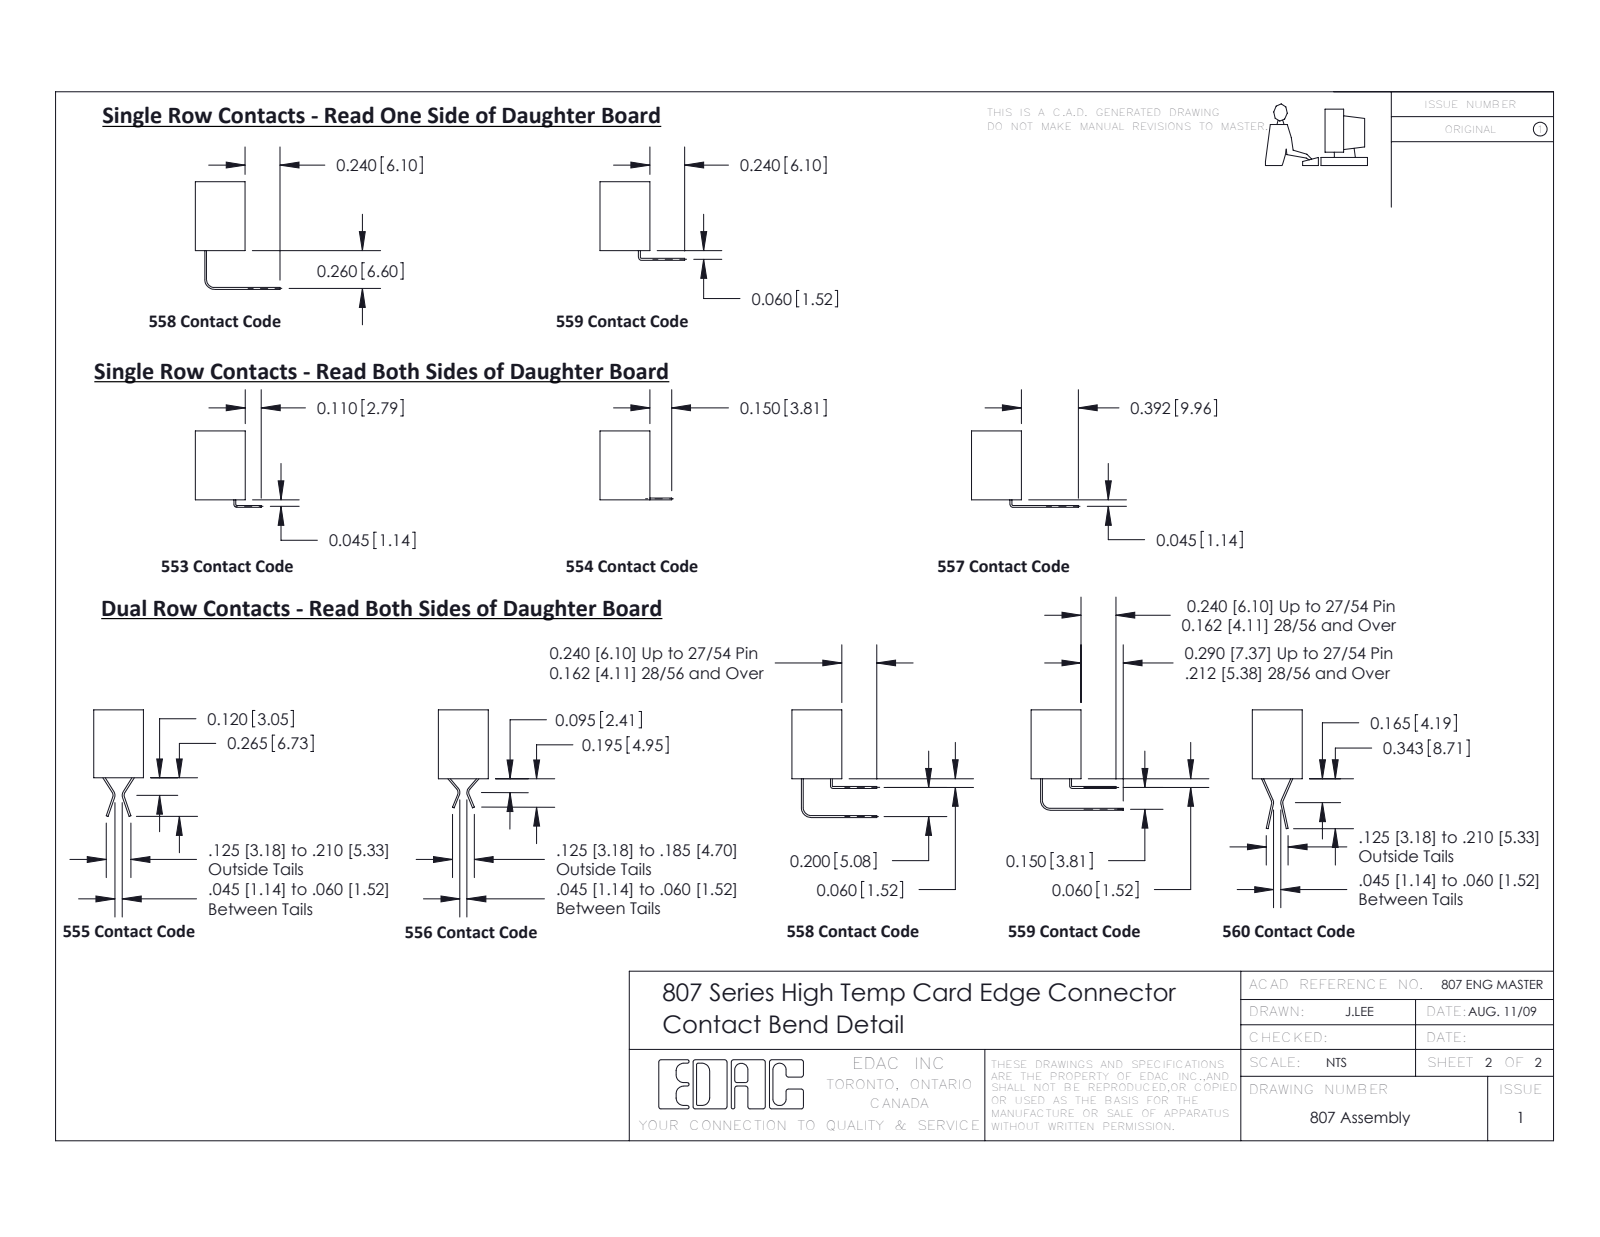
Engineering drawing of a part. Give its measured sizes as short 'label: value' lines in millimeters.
name: 307-290-001_558 559 - 1 (Single); 307-006-558-101; 307-290-001_558 - 2 (Single); 307 Part_No Mounting Lugs
written by: SolidWorks 2016 (CONFIG_CONTROL_DESIGN)
unit: mm
bodies: 3 solids, 317 faces (192 planar, 111 cylindrical, 14 other)
size: 31.6 × 18.9 × 14.8
volume: 2 180 mm³; area: 2 780 mm²
rounds: 25× R0.5, 22× R0.3, 6× R0.2, 6× R0.8, 3× R0.7, 2× R0.3, 2× R0.6, 2× R1.2
face distances: 8.7, 4, 6.2, 3.6, 5.1, 7.9, 7.1, 1.6, 1.6, 5.5
